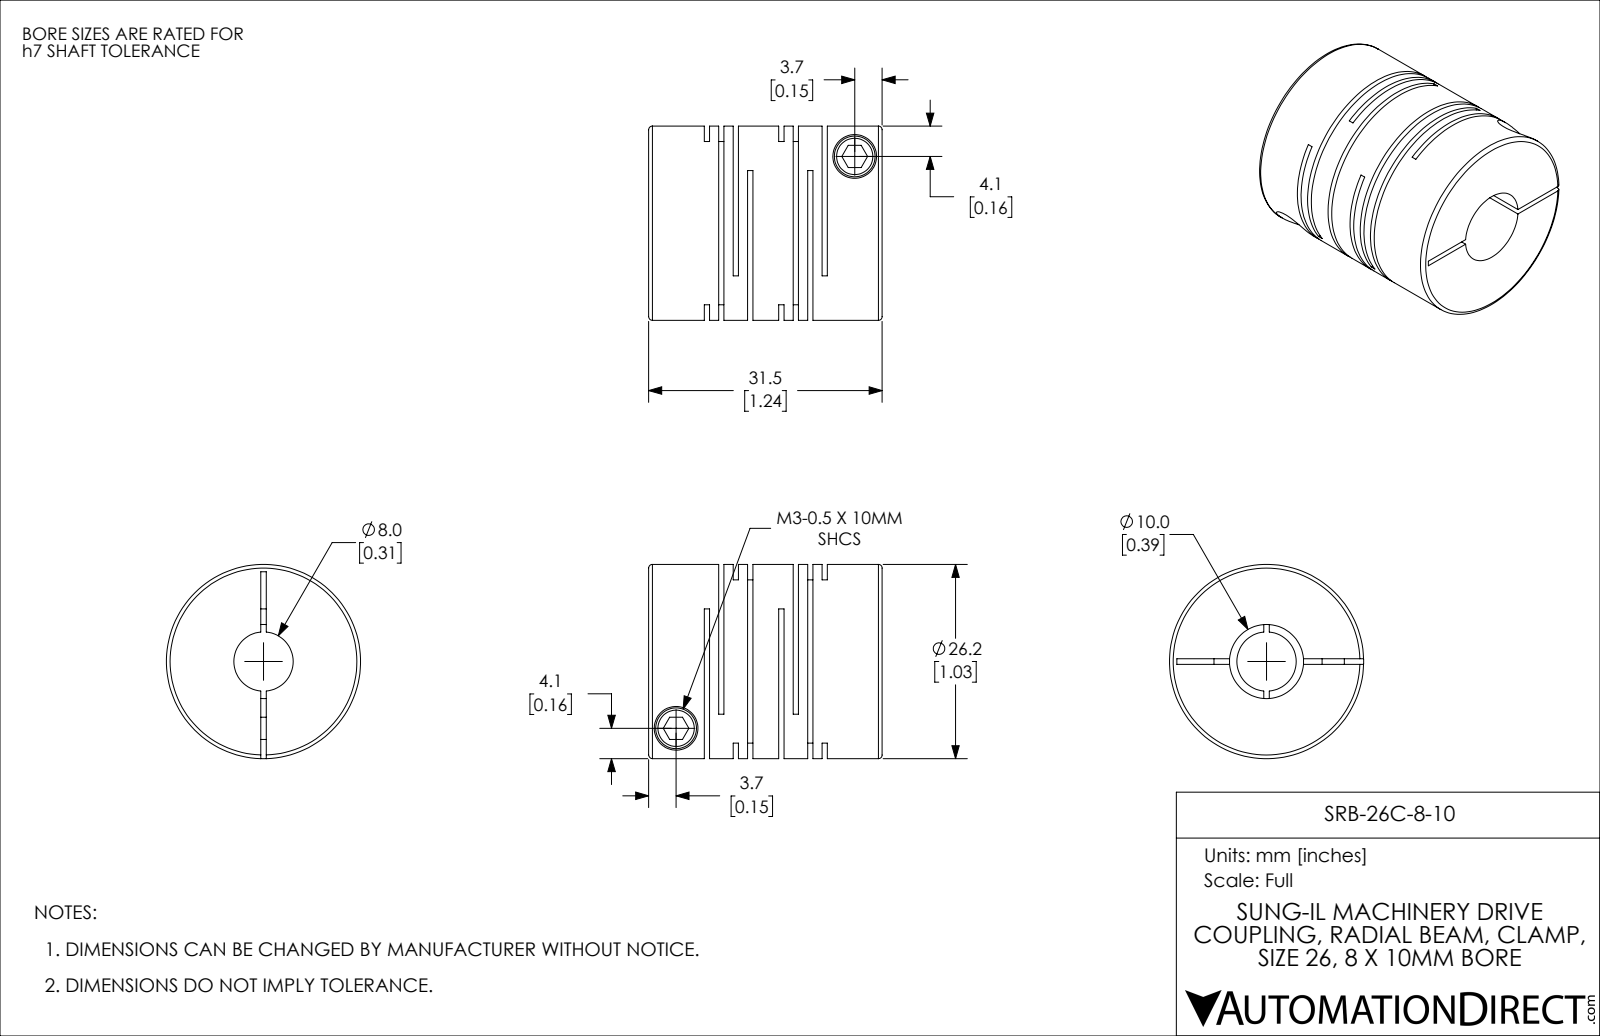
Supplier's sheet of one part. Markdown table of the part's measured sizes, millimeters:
| quantity | value |
| --- | --- |
| part name | SRB-26C-8-10 |
| STEP written by | SolidWorks 2021 (CONFIG_CONTROL_DESIGN) |
| units | millimeters |
| bodies | 1 solid, 114 faces (60 planar, 42 cylindrical, 12 other) |
| overall size | 31.5 × 26.2 × 26.2 |
| volume | 12 144 mm³ |
| surface area | 10 762 mm² |
| round holes (diameter × count) | 3 × 2, 5.9 × 2, 8 × 1, 10 × 1 |
| round bosses / shafts (diameter × count) | 5.5 × 2, 26.2 × 1 |
| main face-to-face distances | 1.95, 10.05, 0.71, 3.9, 8.1, 12, 1.24, 2.66, 9.34, 13.95 |
